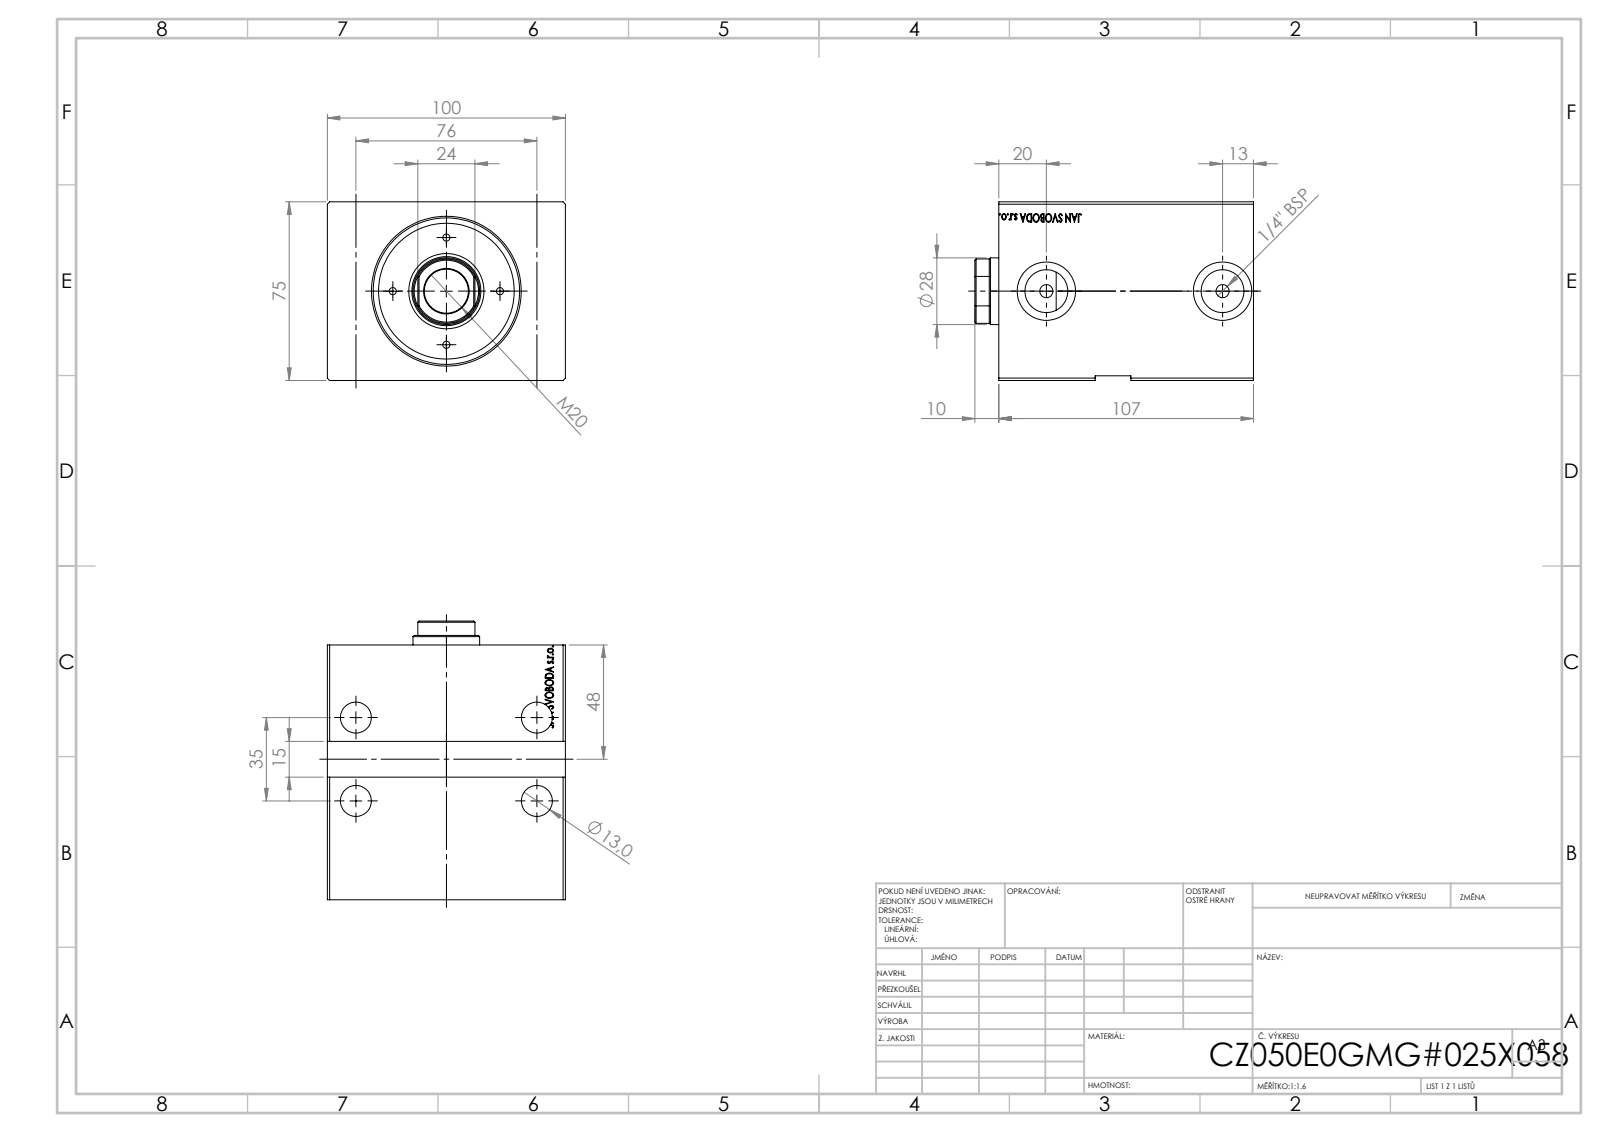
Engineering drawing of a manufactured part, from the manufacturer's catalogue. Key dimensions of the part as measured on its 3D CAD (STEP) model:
STEP written by: SolidWorks 2019 (CONFIG_CONTROL_DESIGN)
Units: millimetres
Bodies: 1 solid, 775 faces (375 planar, 30 cylindrical, 370 other)
Overall size (bounding box): 107 × 100 × 75
Volume: 567 149 mm³ · Surface area: 79 686 mm²
Round holes (diameter × count): ⌀13 ×4, ⌀5.5 ×2, ⌀8 ×2, ⌀18 ×2, ⌀24.5 ×2, ⌀36 ×1, ⌀50 ×1, ⌀61.5 ×1
Main face-to-face distances: 75, 100, 107, 89.2, 17.8, 2, 73, 106.8, 17.6, 10
Hole centre spacings: 35, 76, 83.67, 21.03, 23.58, 34.82, 41, 51.54
